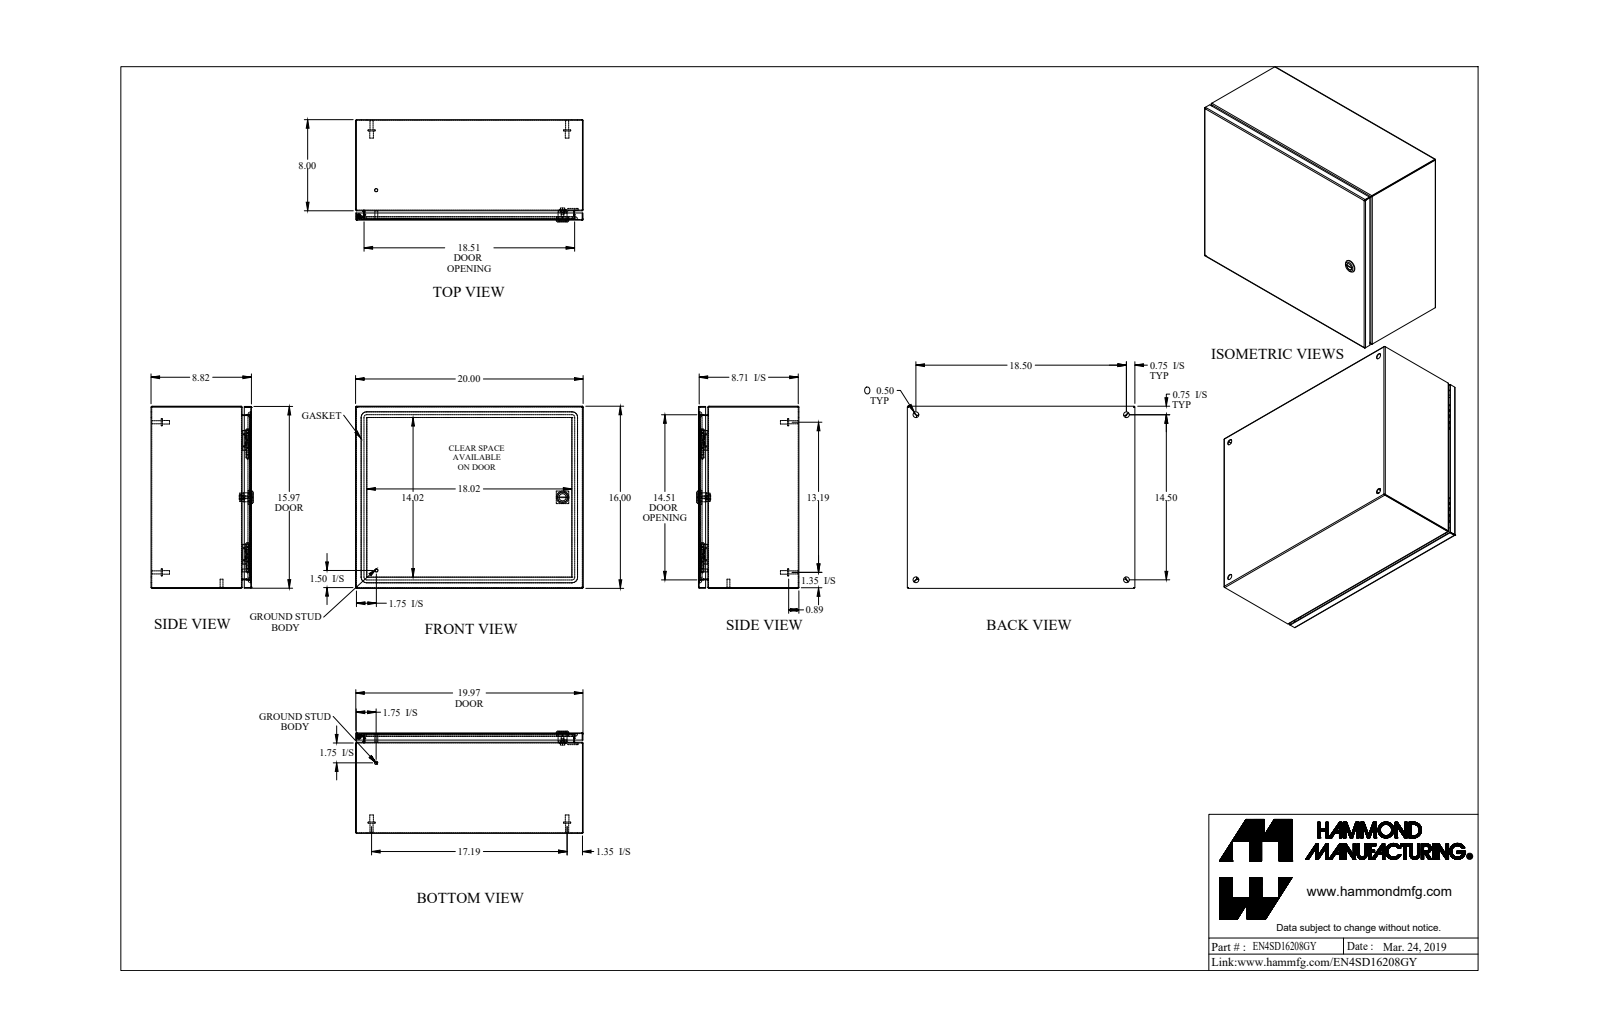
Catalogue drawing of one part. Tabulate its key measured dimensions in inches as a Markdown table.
| quantity | value |
| --- | --- |
| part name | EN4SD16208GY_Default |
| STEP written by | SolidWorks 2019 (CONFIG_CONTROL_DESIGN) |
| units | inches |
| bodies | 21 solids, 634 faces (285 planar, 213 cylindrical, 136 other) |
| overall size | 20 × 16 × 8.982 |
| volume | 84.45 in³ |
| surface area | 2 872 in² |
| round holes (diameter × count) | 0.5 × 4, 0.172 × 1, 0.232 × 1, 0.24 × 1, 0.242 × 1, 0.625 × 1, 0.785 × 1 |
| round bosses / shafts (diameter × count) | 0.625 × 4, 0.313 × 4, 0.27 × 4, 0.281 × 2, 0.25 × 2, 1.1 × 1, 0.525 × 1, 0.455 × 1 |
| partial cylindrical surfaces (radius × count) | 0.029 × 21, 0.086 × 21, 0.25 × 16, 19 × 8, 0.006 × 4, 0.062 × 4, 0.499 × 4, 0.125 × 2 |
| main face-to-face distances | 0.057, 8.765, 8.708, 8.822, 15.943, 19.943, 15.886, 16, 19.886, 20 |
| hole center spacings | 14.5, 18.5, 18.888, 23.506, 7.326, 7.327 |
